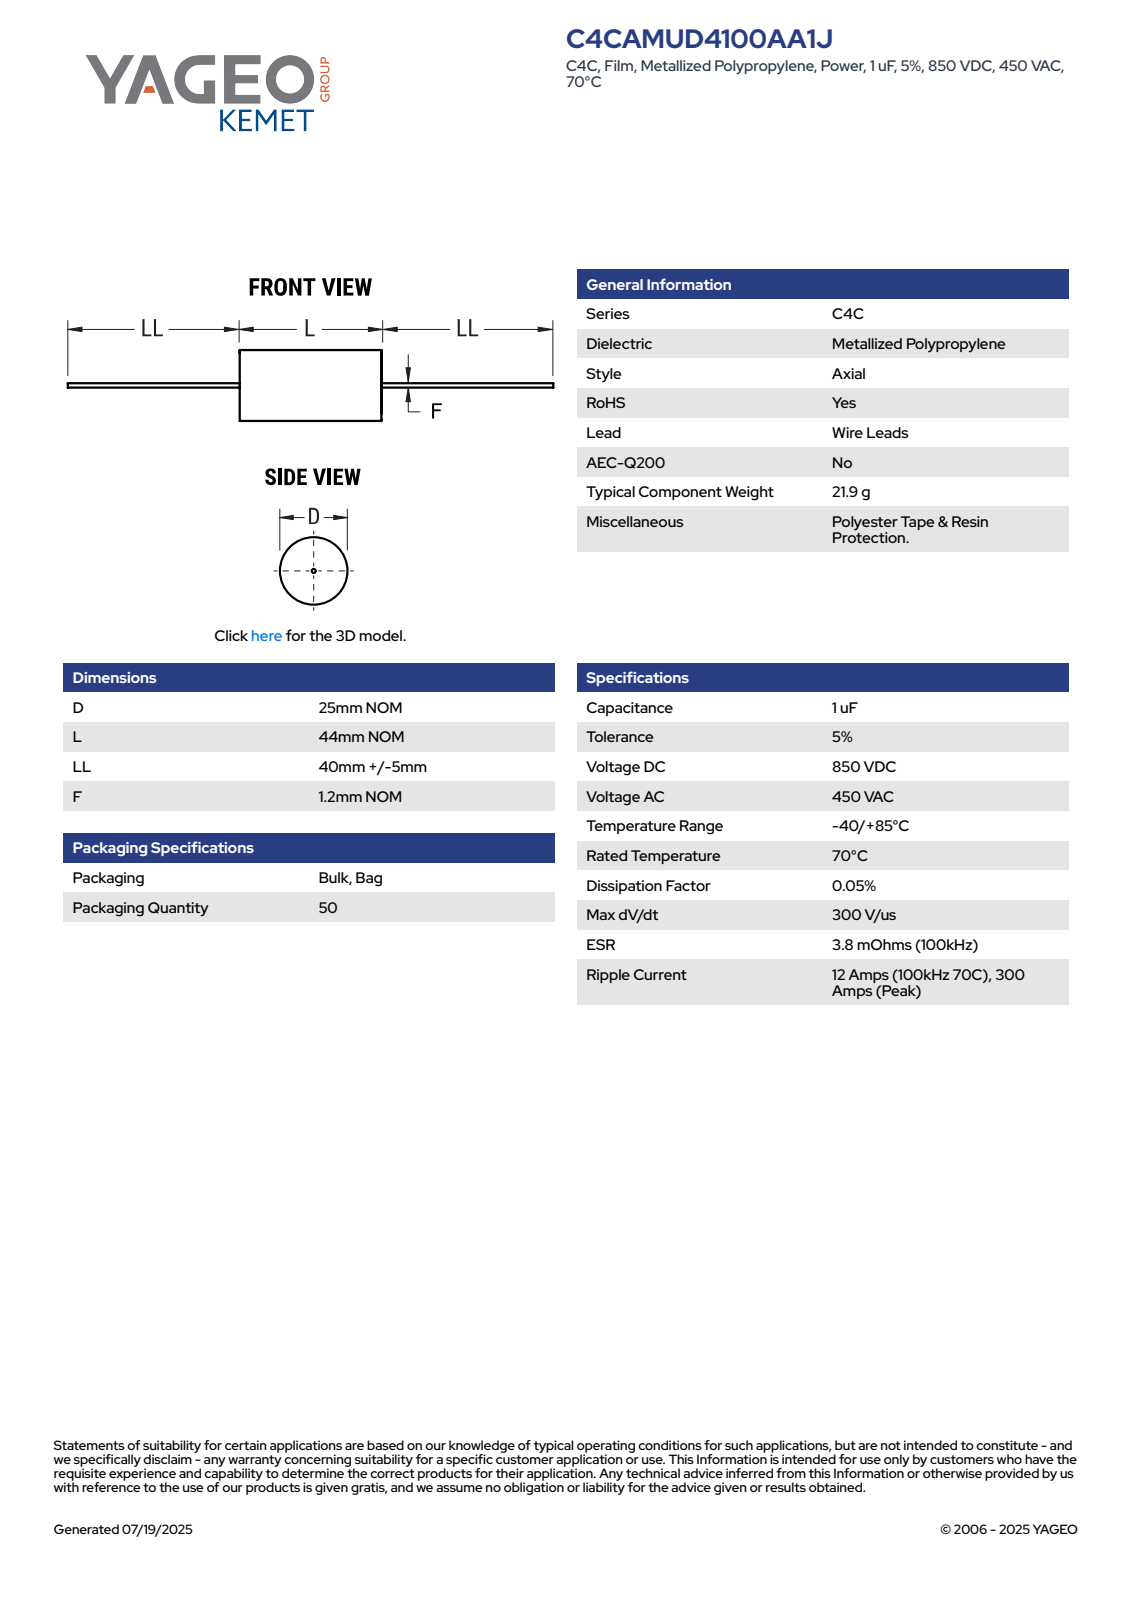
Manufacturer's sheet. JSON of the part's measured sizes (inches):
{"part_name": "CFP_ACWF_25X44_D25L44LL45F1.2", "step_written_by": "SolidWorks 2014 (AUTOMOTIVE_DESIGN)", "units": "inches", "bodies": {"solids": 2, "faces": 87, "planar": 28, "cylindrical": 28, "other": 31}, "overall_size": [5.276, 0.984, 0.984], "volume_in3": 1.324, "surface_area_in2": 8.923, "round_bosses_or_shafts": [[0.984, 1], [0.047, 1]], "partial_cylinders_radius": [[0.492, 1]], "face_to_face_distances": [1.732, 1.732, 1.771, 1.772, 3.504, 5.276, 3.504, 3.504, 1.772]}
